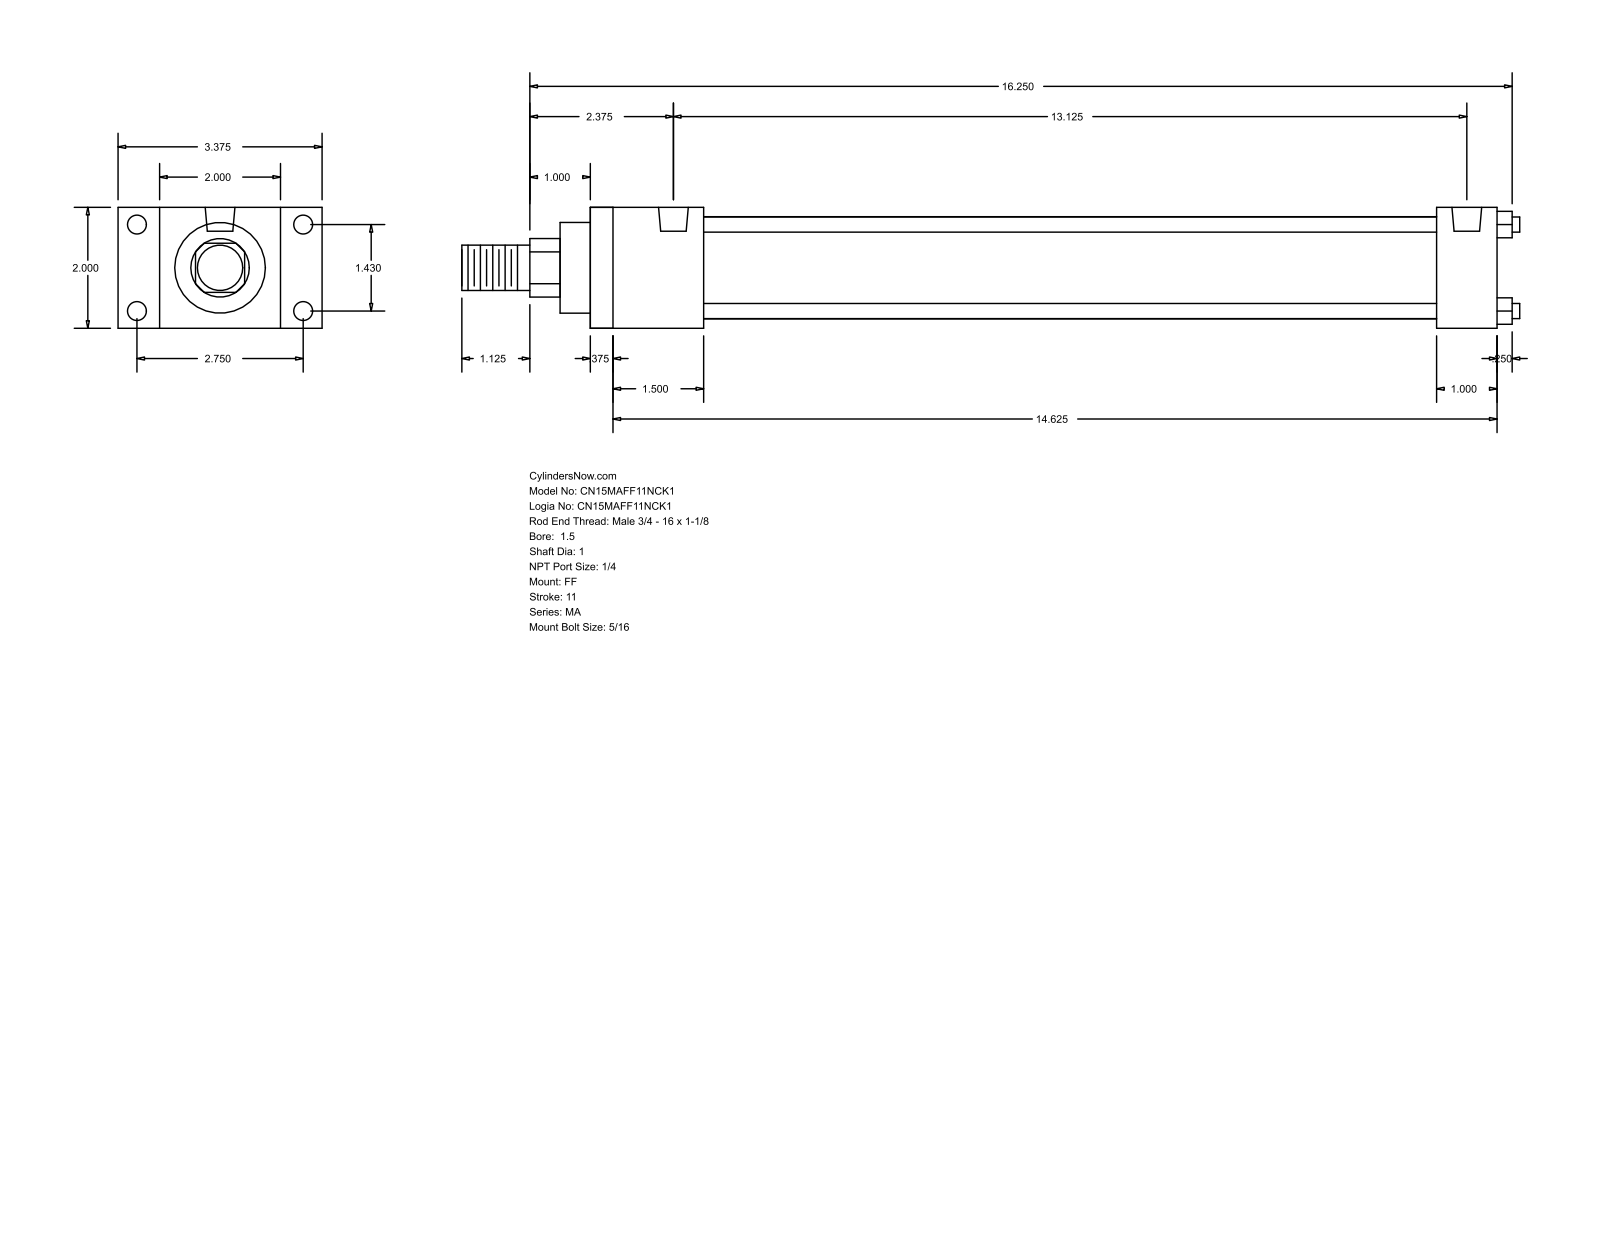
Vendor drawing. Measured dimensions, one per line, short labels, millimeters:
name: MA_FF__0150_1
written by: GSSL Pune (CONFIG_CONTROL_DESIGN)
unit: mm
bodies: 0 solids, 92 faces (64 planar, 28 cylindrical, 0 other)
size: 444.5 × 85.72 × 50.8
holes: 8× ⌀7.94, 2× ⌀12.49
bosses: 4× ⌀6.35, 1× ⌀42.93, 1× ⌀38.1, 1× ⌀25.4, 1× ⌀19.05
rounds: 1× R12.29
face distances: 50.8, 381, 9.52, 371.48, 25.4, 47.63, 355.6, 38.11, 346.08, 307.97
hole spacings: 36.32, 69.84, 78.72, 333.37
